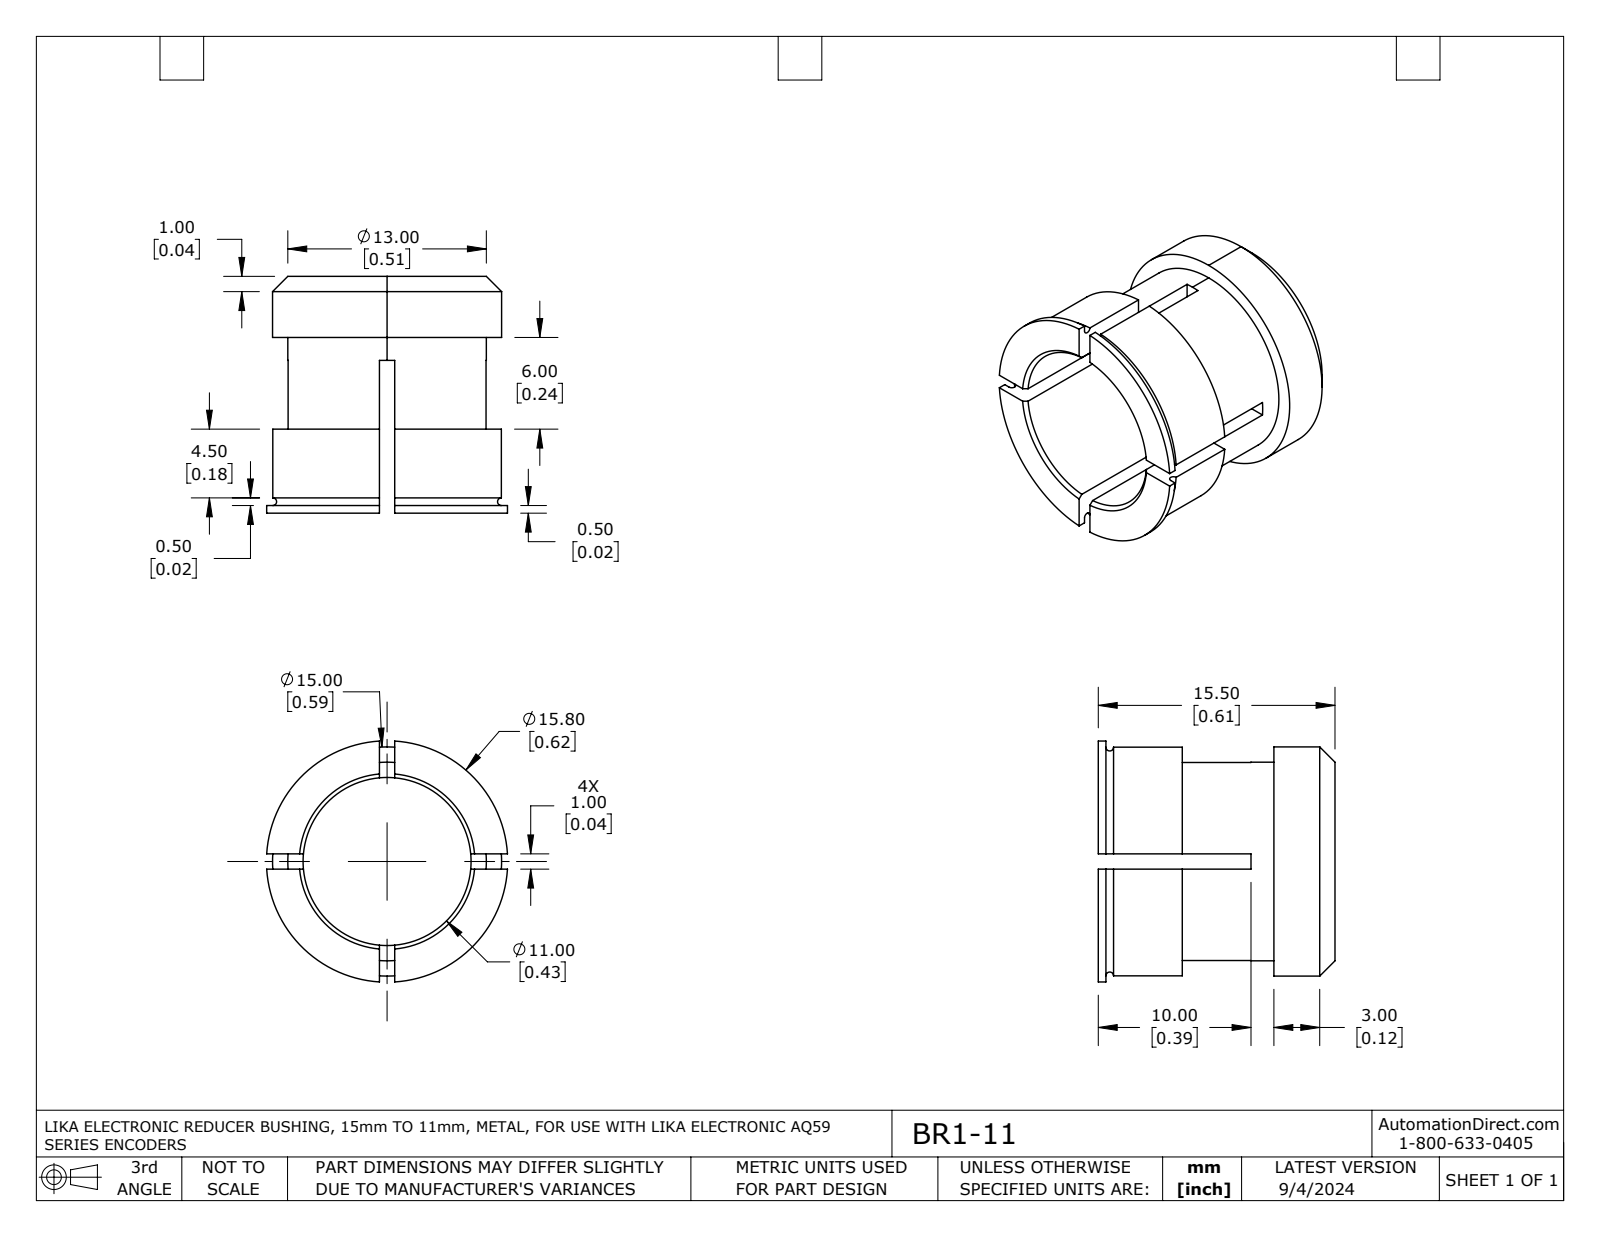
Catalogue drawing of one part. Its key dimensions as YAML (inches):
part_name: "BR1-11"
step_written_by: "SolidWorks 2021 (AUTOMOTIVE_DESIGN)"
units: inches
bodies: {solids: 1, faces: 54, planar: 26, cylindrical: 17, other: 11}
overall_size: [0.621, 0.621, 0.61]
volume: 0.056
surface_area: 2.374
round_holes:
  - {diameter: 0.433, count: 1}
round_bosses_or_shafts:
  - {diameter: 0.622, count: 1}
  - {diameter: 0.591, count: 1}
  - {diameter: 0.512, count: 1}
face_to_face_distances: [0.039, 0.217, 0.453, 0.394, 0.236, 0.157, 0.61, 0.591, 0.433, 0.197]
